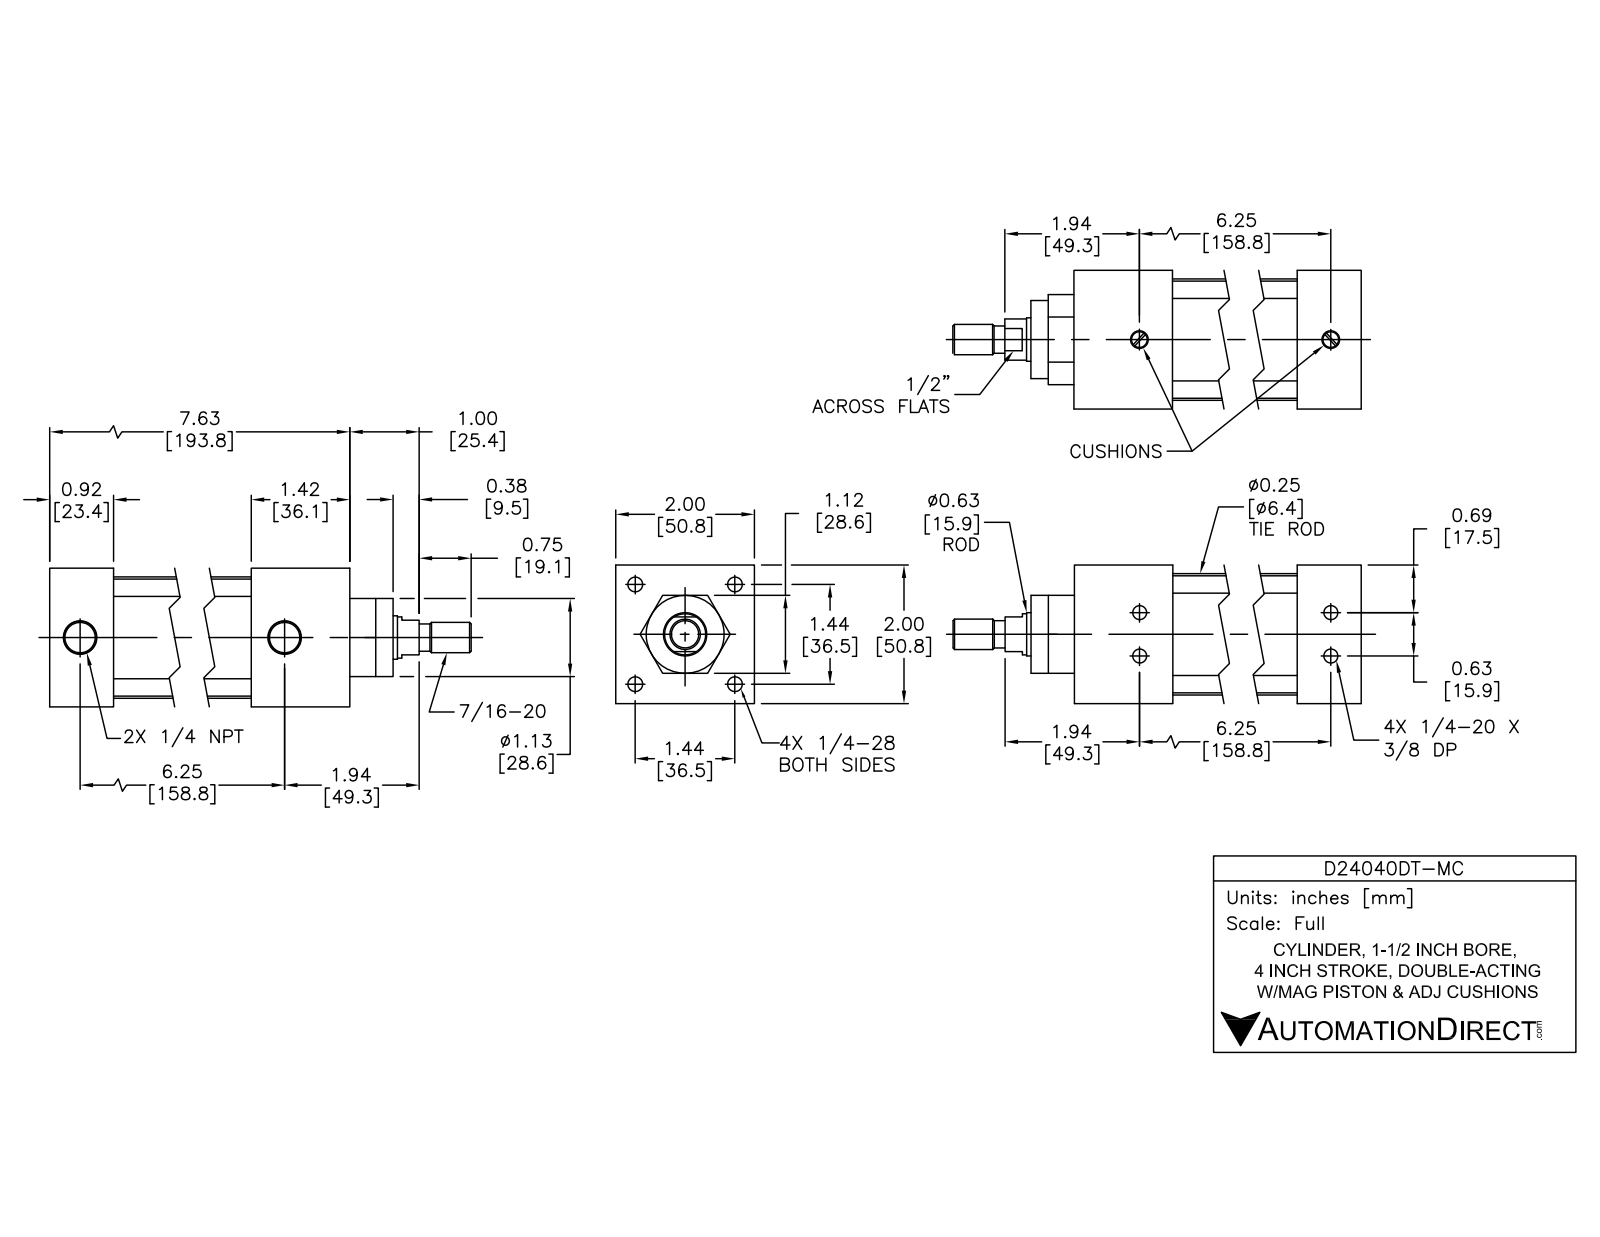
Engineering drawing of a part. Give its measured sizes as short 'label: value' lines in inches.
name: D24040DT-MC; D24040DT-M PISTON; D24040DT-M BODY
written by: SolidWorks 2015 (AUTOMOTIVE_DESIGN)
unit: in
bodies: 12 solids, 303 faces (99 planar, 114 cylindrical, 90 other)
size: 9.371 × 2 × 2
volume: 17.08 in³; area: 152.9 in²
holes: 4× ⌀0.196, 4× ⌀0.211, 4× ⌀0.281, 4× ⌀0.406, 2× ⌀0.297, 2× ⌀0.477, 1× ⌀0.625, 1× ⌀0.628, 1× ⌀1.5
bosses: 4× ⌀0.39, 4× ⌀0.25, 4× ⌀0.222, 1× ⌀1.75, 1× ⌀1.497, 1× ⌀1.121, 1× ⌀0.622, 1× ⌀0.59
rounds: 4× R0.2
face distances: 2, 7.621, 1.42, 6.201, 6.701, 5.281, 0.92, 1.121, 6.601, 5.181
hole spacings: 0.313, 1.014, 1.434, 0.625, 2.028, 6.247, 6.254, 6.254
